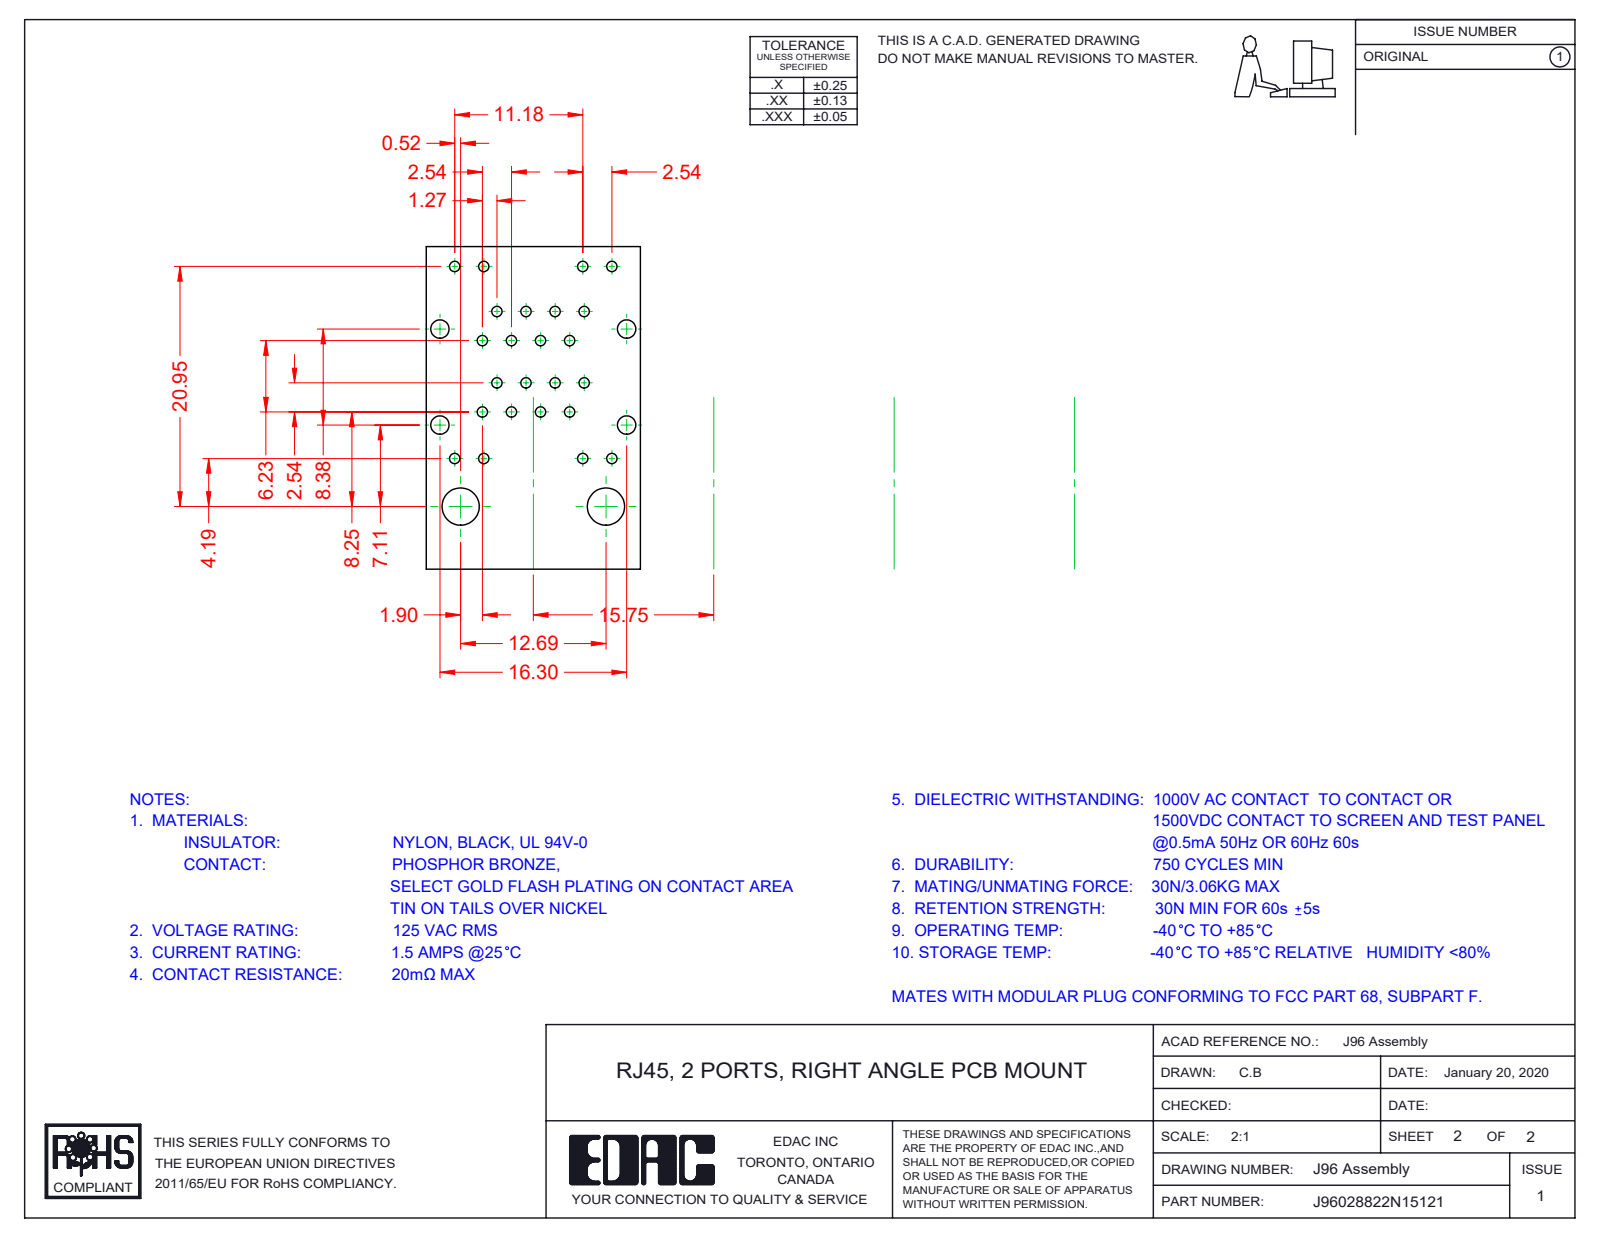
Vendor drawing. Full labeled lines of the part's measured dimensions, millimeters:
Part name (STEP PRODUCT): J96028822N15121; 96 Grounding_2 Ports; 96 Back Plate_2 Ports; 96 Insulator_2 Ports (+8 more)
STEP written by: SolidWorks 2016 (CONFIG_CONTROL_DESIGN)
Units: millimetres
Bodies: 27 solids, 2386 faces (1849 planar, 431 cylindrical, 106 other)
Overall size (bounding box): 29.58 × 28.68 × 16.8
Volume: 6 852 mm³ · Surface area: 19 109 mm²
Partial cylindrical surfaces — rounded edges, fillets, slot ends (radius × count): R0.25 ×48, R0.15 ×32, R0.35 ×24, R0.5 ×16, R1 ×16, R0.2 ×13, R0.7 ×9, R2 ×5
Main face-to-face distances: 16.3, 16.1, 1.75, 16.5, 14.75, 1.55, 14.55, 0.53, 1.48, 11.2
